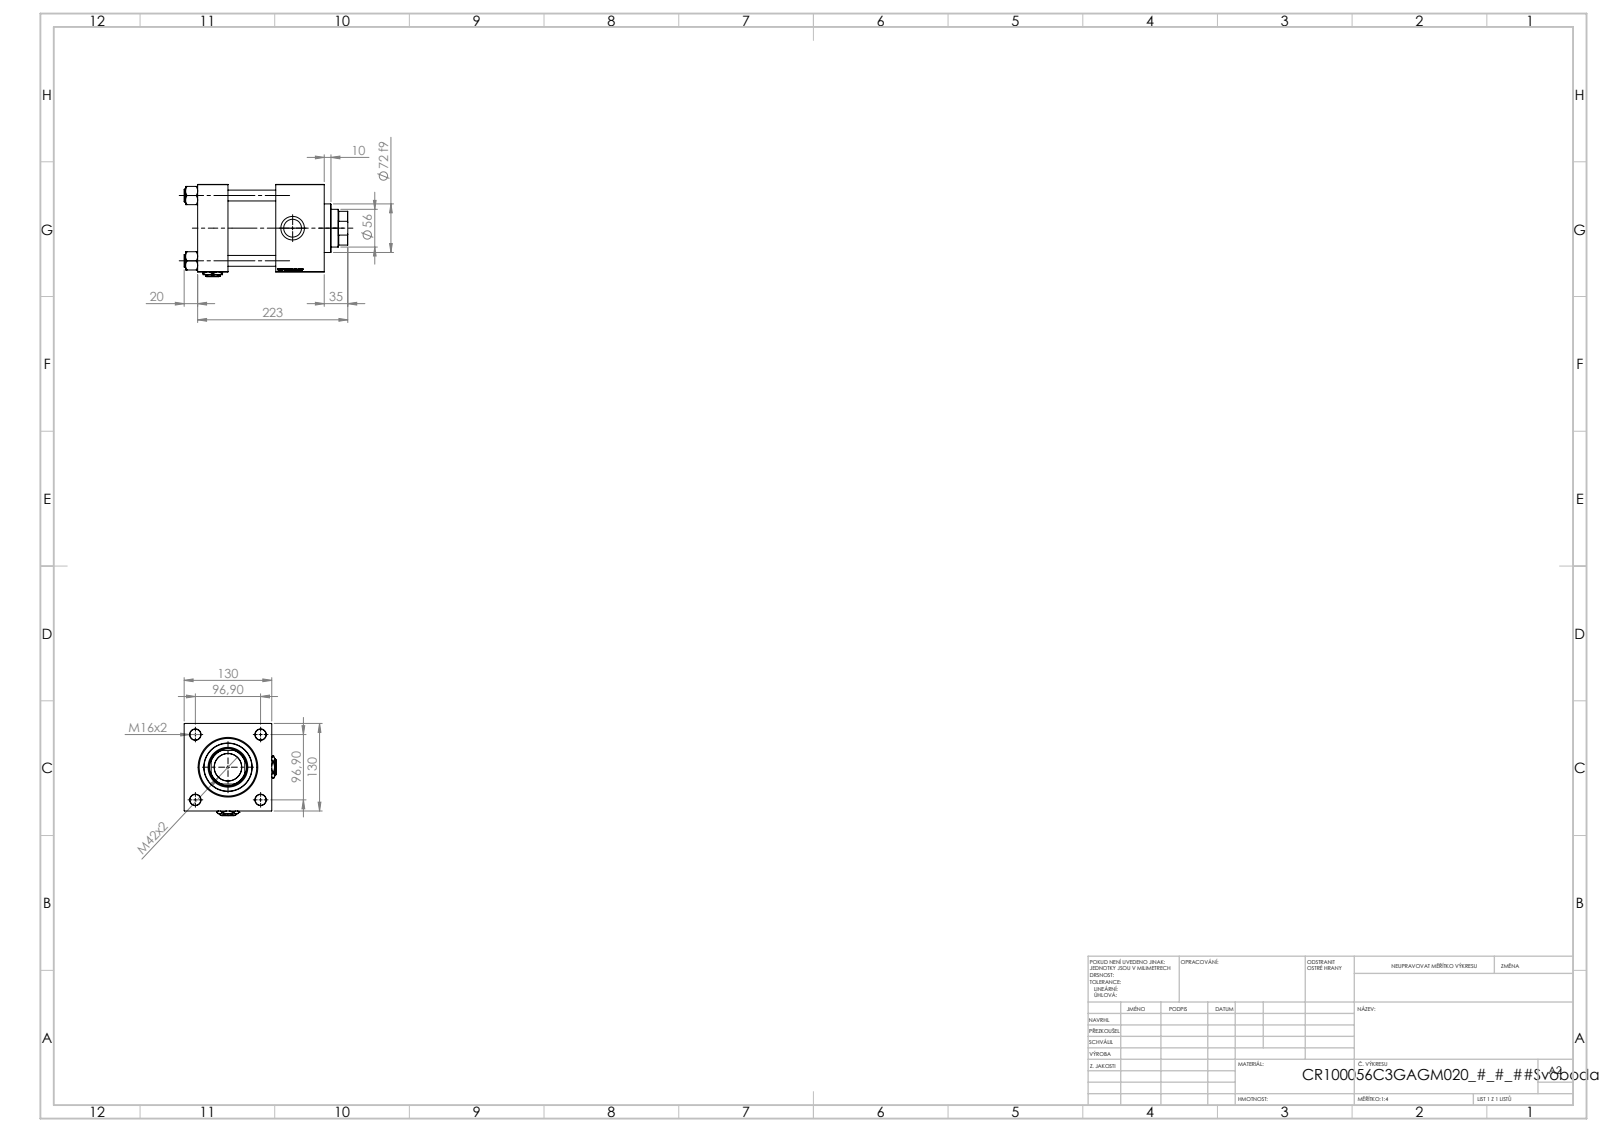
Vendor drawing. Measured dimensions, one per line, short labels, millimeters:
name: V215CR_C_TYCINKA; V215CR_C_Body; V215_VC_A; NUT_M5_C (+2 more)
written by: SolidWorks 2019 (CONFIG_CONTROL_DESIGN)
unit: mm
bodies: 13 solids, 1297 faces (621 planar, 98 cylindrical, 578 other)
size: 243 × 137 × 137
volume: 2 460 000 mm³; area: 340 584 mm²
holes: 4× ⌀16, 2× ⌀7, 2× ⌀26.44, 2× ⌀35, 1× ⌀40.5, 1× ⌀56, 1× ⌀59, 1× ⌀76, 1× ⌀85.5, 1× ⌀100
bosses: 4× ⌀19, 1× ⌀106, 1× ⌀72
rounds: 1× R27
face distances: 130, 45, 188, 143, 116, 71, 72, 20, 51, 92
hole spacings: 68.52, 96.9, 137.04
